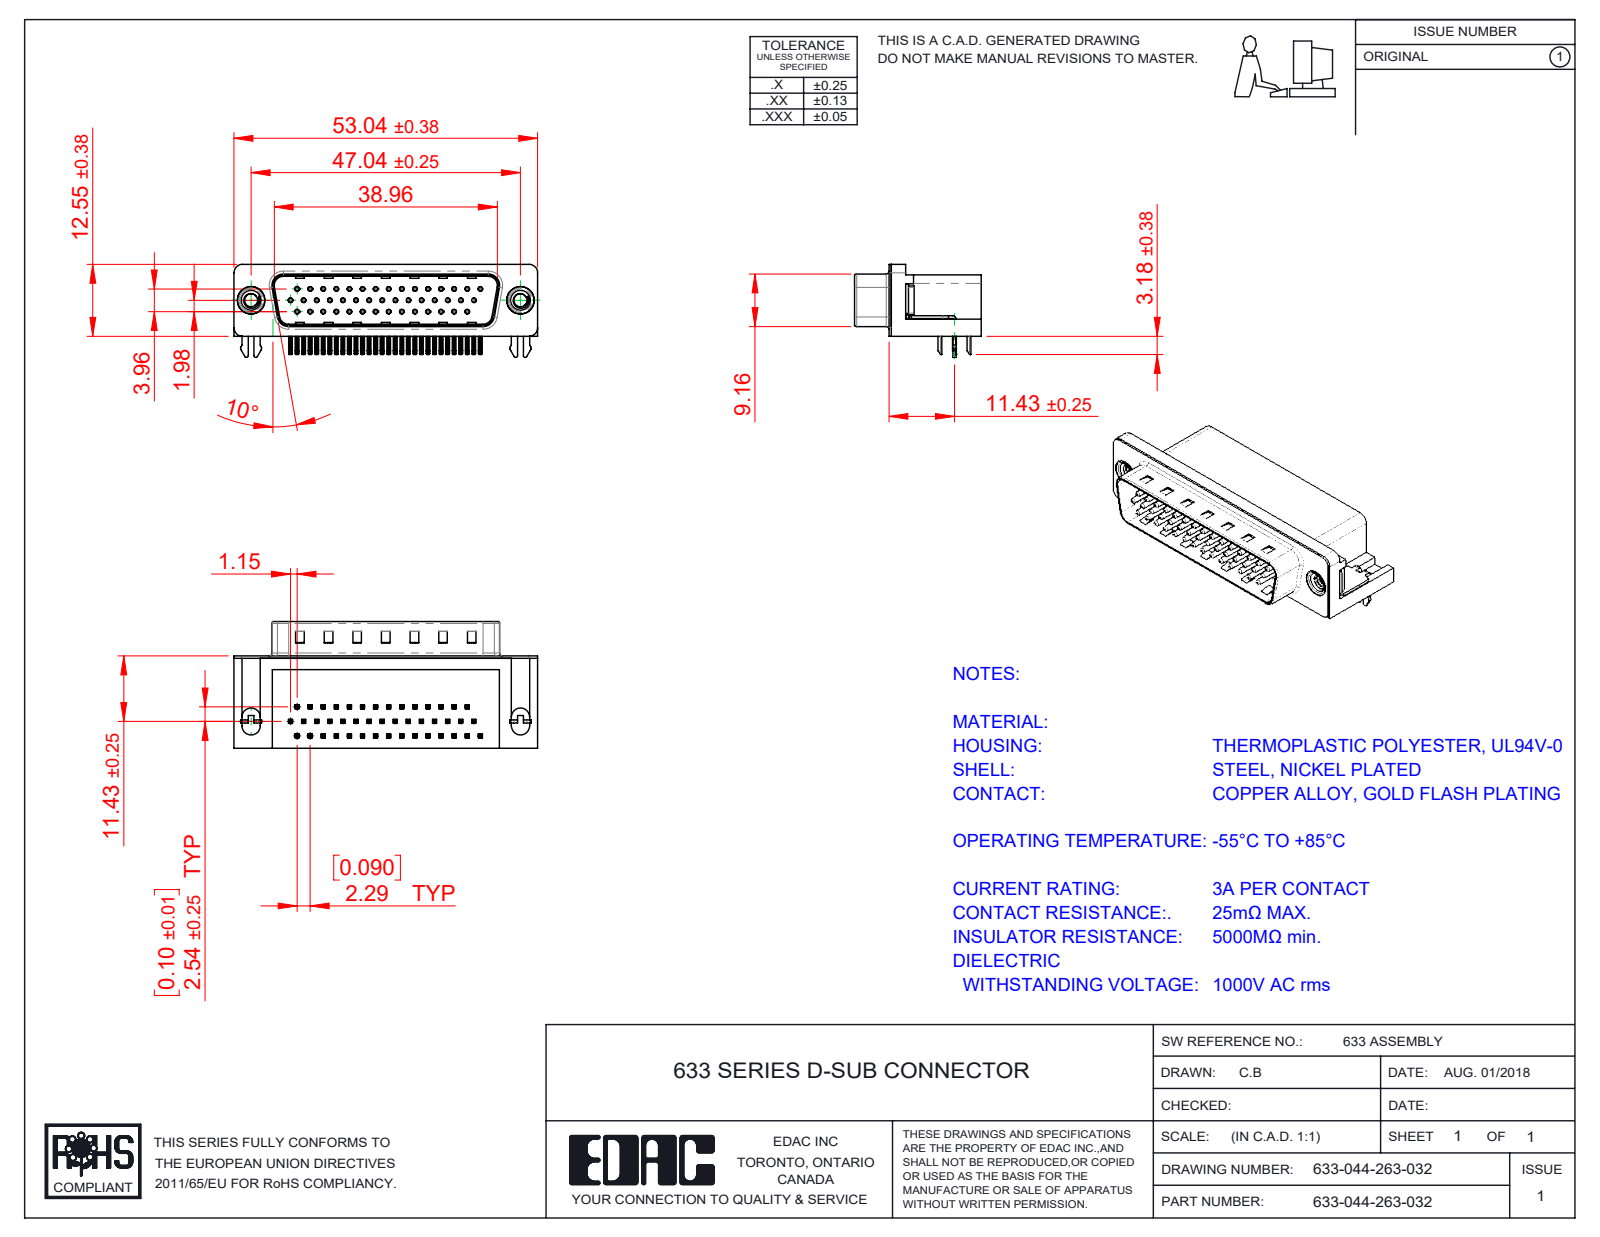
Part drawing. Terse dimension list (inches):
name: 633 4-40 Threaded Rivet; 633 2 Prong Board Lock; 633 Contact Top; 633 Contact Middle (+4 more)
written by: SolidWorks 2016 (CONFIG_CONTROL_DESIGN)
unit: in
bodies: 50 solids, 3730 faces (2349 planar, 1068 cylindrical, 313 other)
size: 2.088 × 0.87 × 0.64
volume: 0.495 in³; area: 15.85 in²
holes: 44× ⌀0.014, 44× ⌀0.031, 2× ⌀0.089, 2× ⌀0.157, 2× ⌀0.189, 2× ⌀0.197
bosses: 44× ⌀0.03, 2× ⌀0.193, 2× ⌀0.187, 2× ⌀0.154
rounds: 184× R0.01, 88× R0.005, 16× R0.039, 14× R0.02, 8× R0.063, 7× R0.059, 4× R0.013, 4× R0.035
face distances: 0.016, 0.407, 0.618, 0.345, 0.114, 0.098, 0.083, 0.634, 0.421, 0.1
hole spacings: 0.09, 0.18, 0.18, 0.09, 0.27, 0.361, 0.451, 0.089
